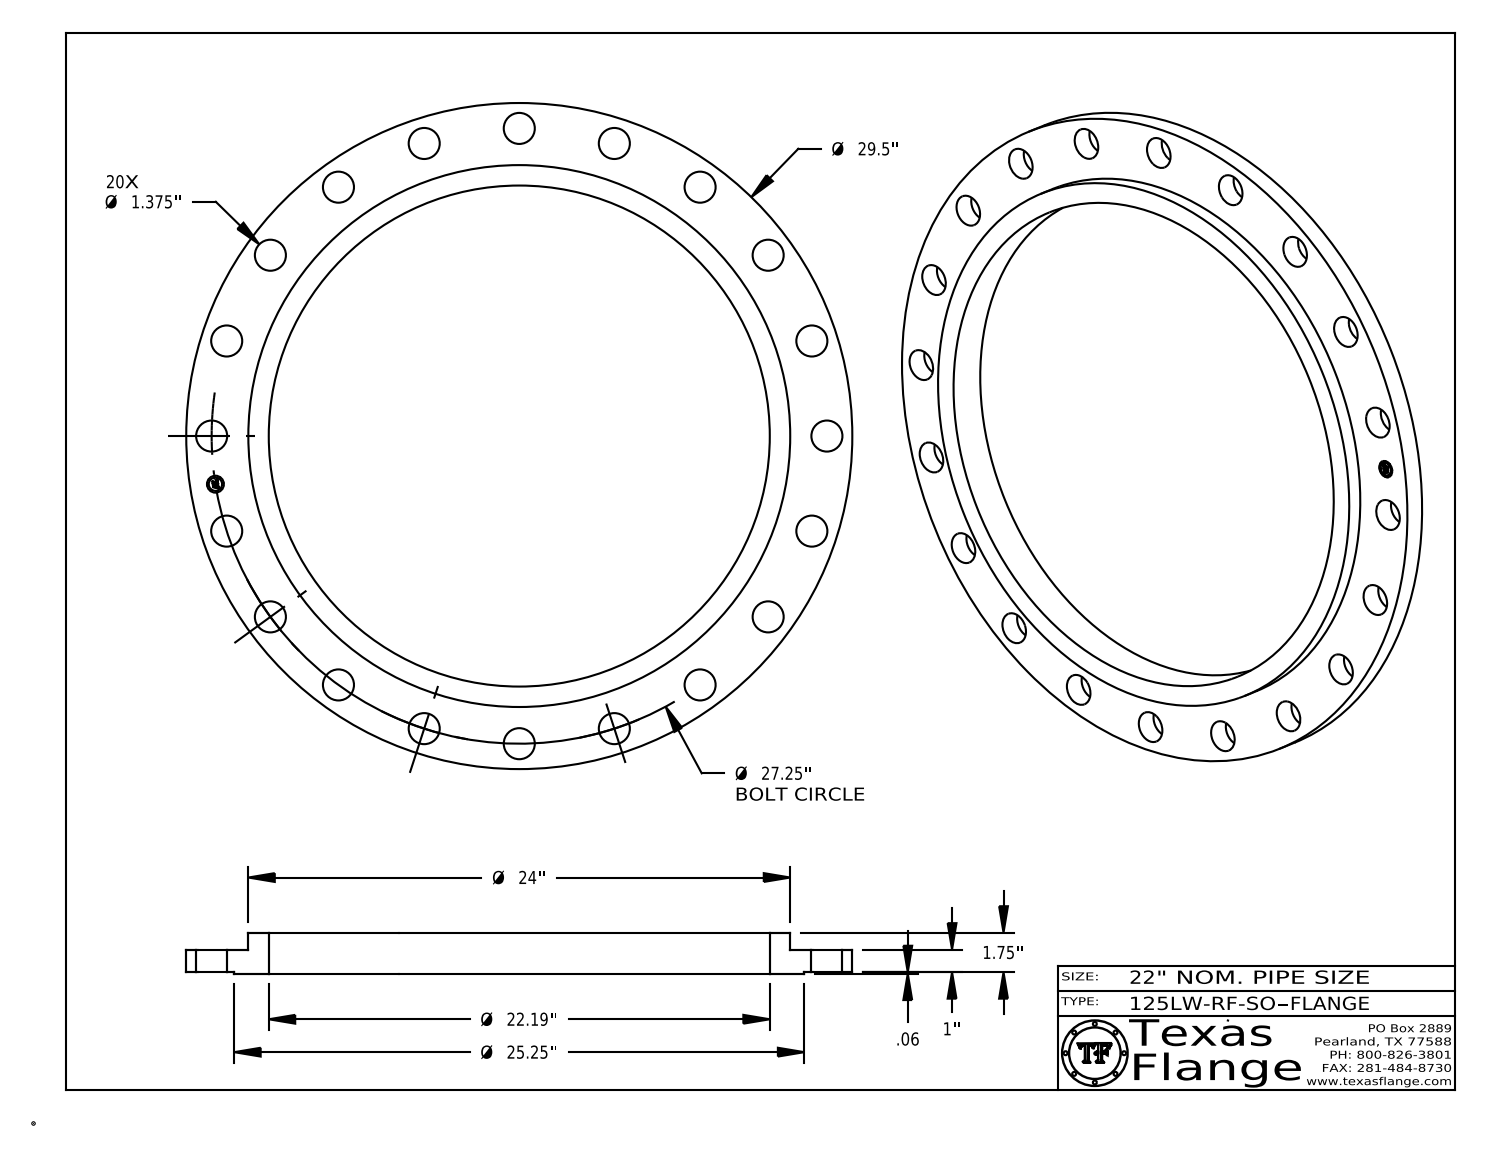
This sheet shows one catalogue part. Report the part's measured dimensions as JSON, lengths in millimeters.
{"part_name": "125LW-RF-SO-B16.1", "step_written_by": "CATIA V5 STEP AP214 (AUTOMOTIVE_DESIGN)", "units": "millimeters", "bodies": {"solids": 1, "faces": 437, "planar": 369, "cylindrical": 68, "other": 0}, "overall_size": [749.3, 749.3, 46.1], "volume_mm3": 5300000, "surface_area_mm2": 581400, "round_holes": [[34.9, 20], [19.1, 1], [563.6, 1]], "round_bosses_or_shafts": [[1.1, 8], [749.3, 1], [641.4, 1], [609.6, 1], [15, 1]], "face_to_face_distances": [25.4, 1.6, 27, 46.1, 44.5, 19.1, 26.6, 25, 0.4, 19.4], "hole_center_spacings": [346.1, 489.4, 658.3, 213.9, 314.2, 108.3, 406.8, 560]}
